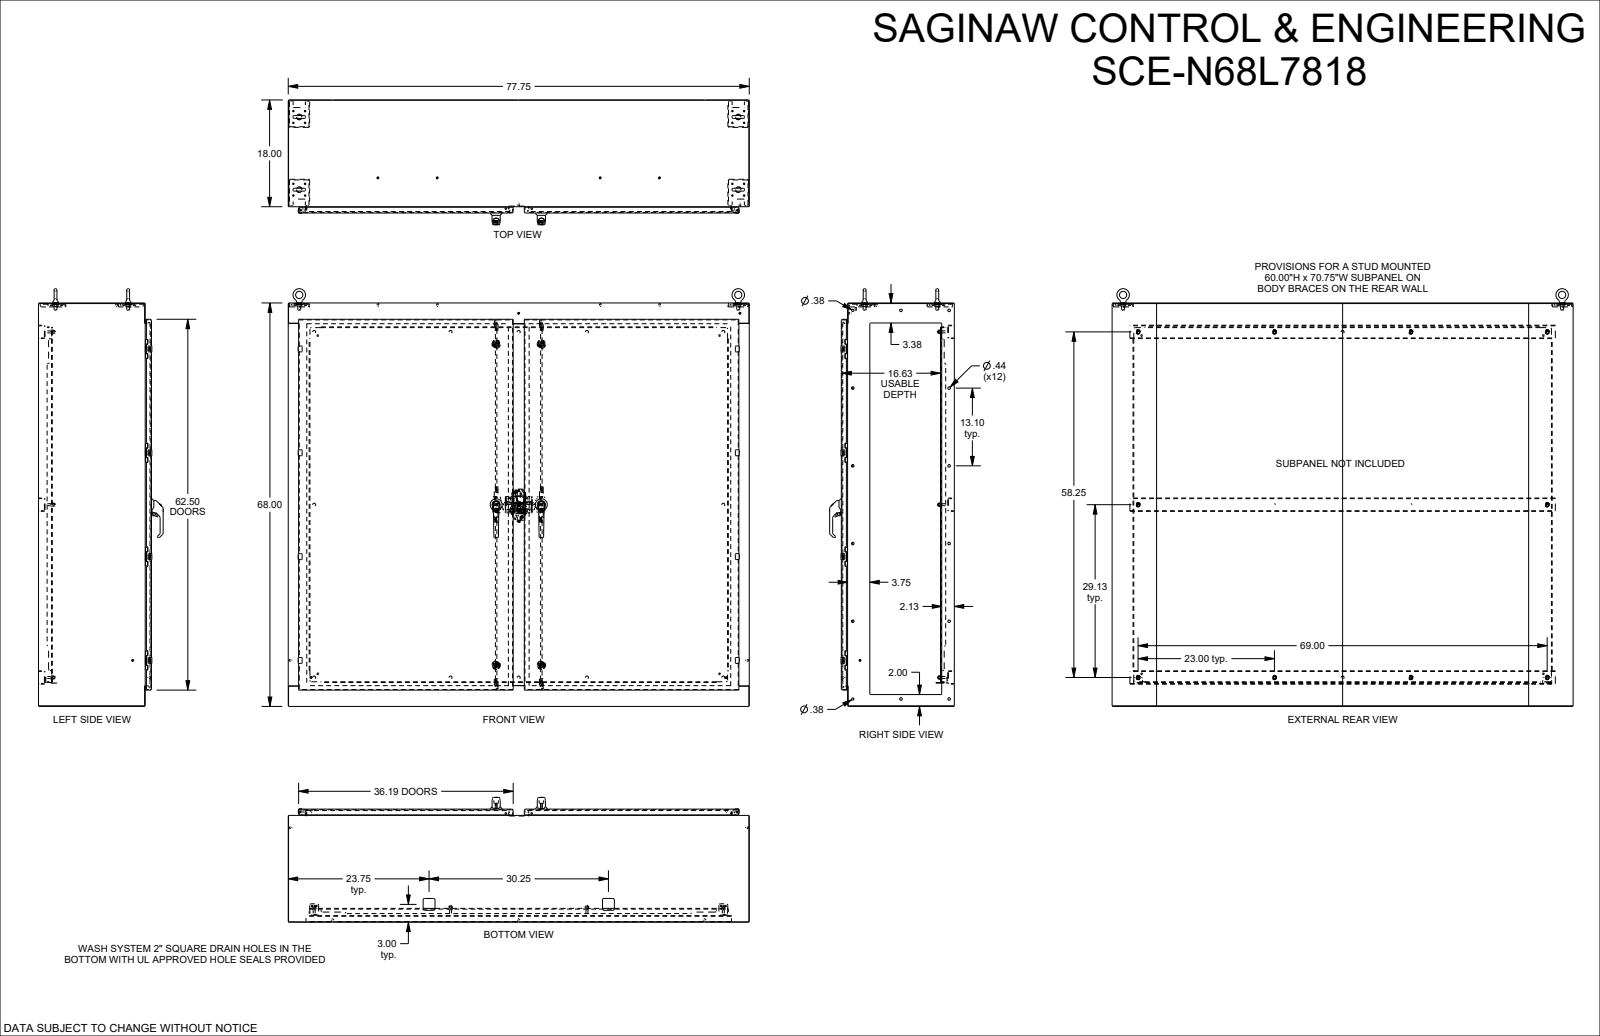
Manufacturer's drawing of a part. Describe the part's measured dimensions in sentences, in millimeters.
The part is named "SCE-N68L7818". Its 3-D file was written by "SolidWorks 2023 (AUTOMOTIVE_DESIGN)". It is 49 solids with 7483 faces: 3045 planar, 2532 cylindrical and 1906 other. Overall it measures 1974.9 by 1802 by 534.6 millimeters. Its volume is 30 580 000 cubic millimeters and its surface area 22 820 000 square millimeters. Round holes: 20 of diameter 6.4, 18 of diameter 9.5, 16 of diameter 5.2, 16 of diameter 6.2, 12 of diameter 11.1, 8 of diameter 1, 8 of diameter 4.3, 8 of diameter 5.5, 4 of diameter 4, 4 of diameter 6.5, 4 of diameter 8.7, 4 of diameter 8.7. Round bosses or shafts: 24 of diameter 4.3, 20 of diameter 6.4, 16 of diameter 6.1, 10 of diameter 5, 4 of diameter 35.6, 4 of diameter 29.8, 4 of diameter 15.2, 4 of diameter 8.7. Partial cylindrical surfaces (rounded edges, fillets, slot ends): 223 of radius 0.8, 166 of radius 0.4, 100 of radius 3.2, 72 of radius 0.5, 68 of radius 1.6, 48 of radius 0.5, 42 of radius 1, 42 of radius 1. The main face-to-face distances are 2.6, 481.4, 484.1, 478.8, 1724.6, 454.6, 26.9, 1727.2, 1721.9, 451.9. The hole center spacings are 50.3, 332.7, 530.2, 35.6, 665.5, 783.1, 725.1, 782.2.
